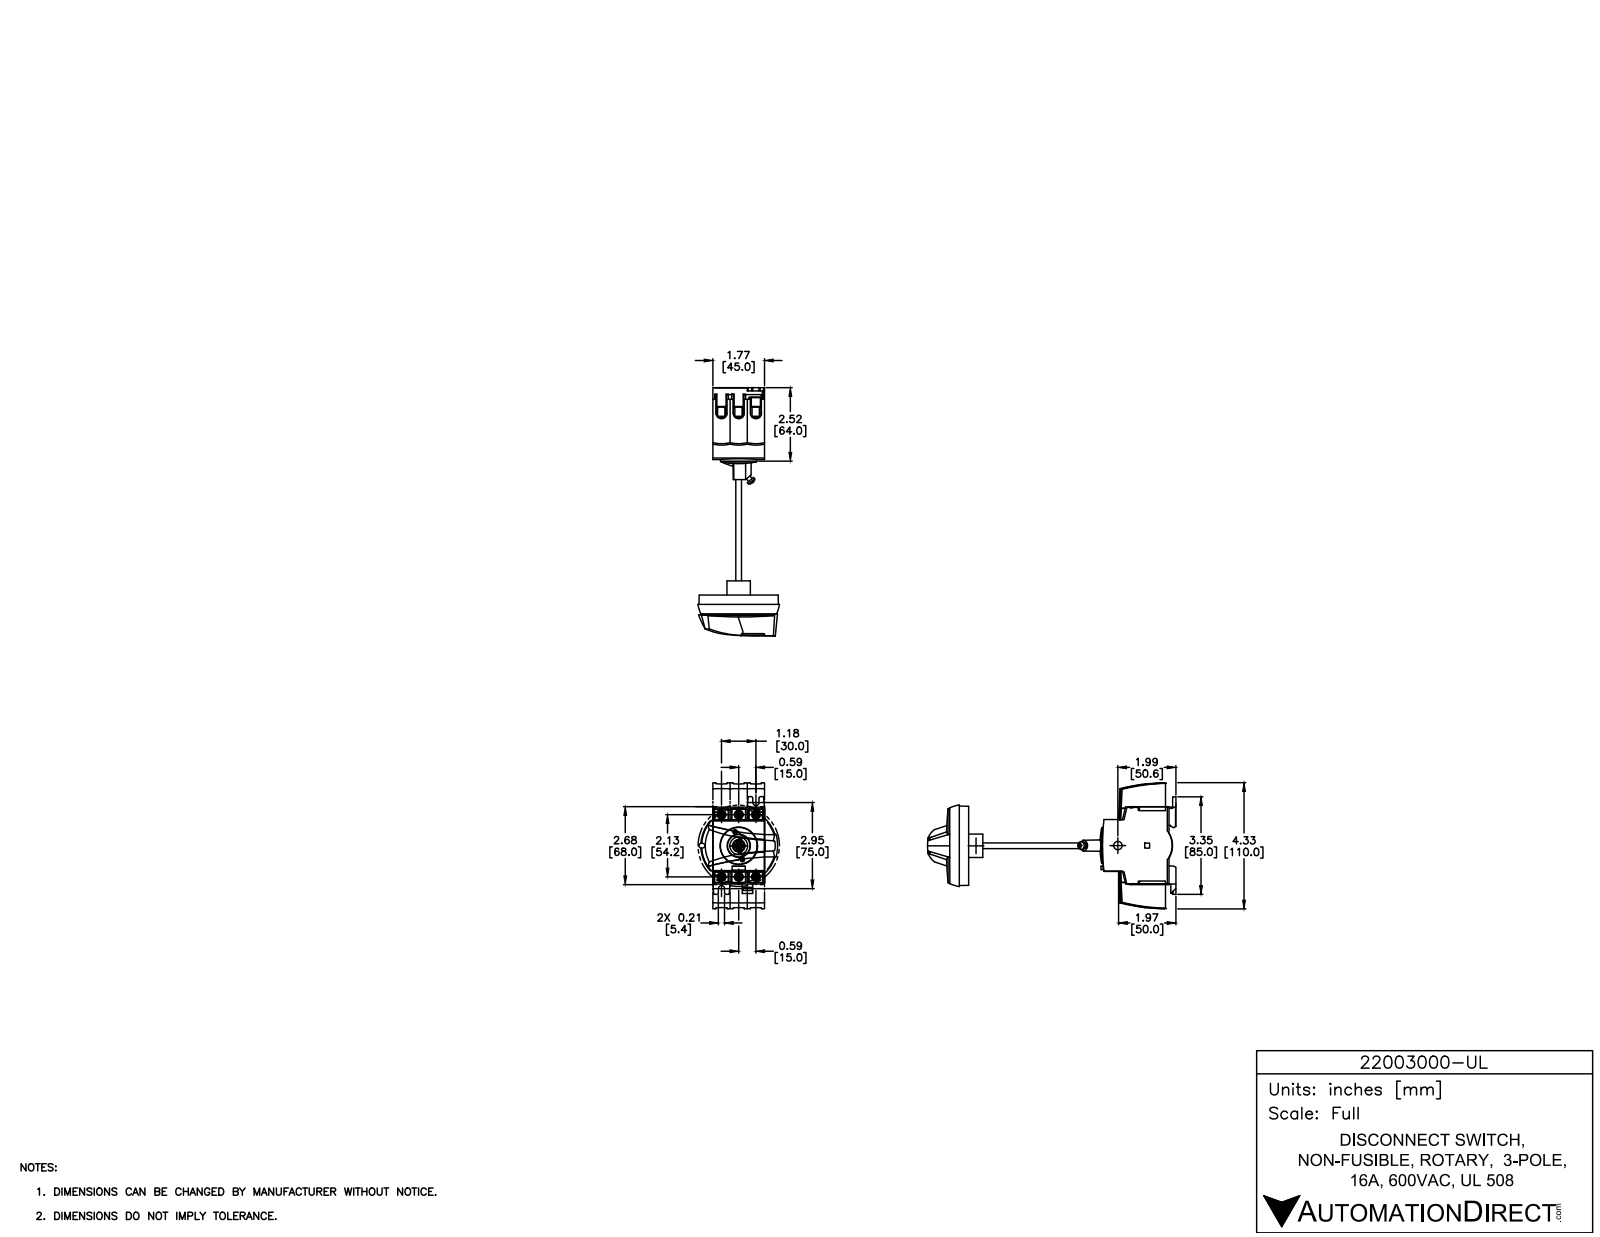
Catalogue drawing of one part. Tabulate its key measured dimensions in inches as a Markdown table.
| quantity | value |
| --- | --- |
| part name | 22003000-UL |
| STEP written by | SolidWorks 2015 (AUTOMOTIVE_DESIGN) |
| units | inches |
| bodies | 1 solid, 463 faces (389 planar, 50 cylindrical, 24 other) |
| overall size | 3.346 × 2.571 × 1.772 |
| volume | 9.498 in³ |
| surface area | 40.23 in² |
| round holes (diameter × count) | 0.26 × 6, 0.283 × 1, 1.244 × 1 |
| partial cylindrical surfaces (radius × count) | 0.012 × 13, 0.02 × 5, 0.165 × 4, 0.039 × 3, 0.106 × 2, 0.13 × 1, 0.354 × 1, 0.37 × 1 |
| main face-to-face distances | 1.772, 0.433, 2.205, 2.157, 2.638, 2.28, 0.591, 2.591, 0.047, 0.386 |
| hole center spacings | 0.591, 1.219, 2.214, 2.134, 1.067, 1.181, 2.439 |
